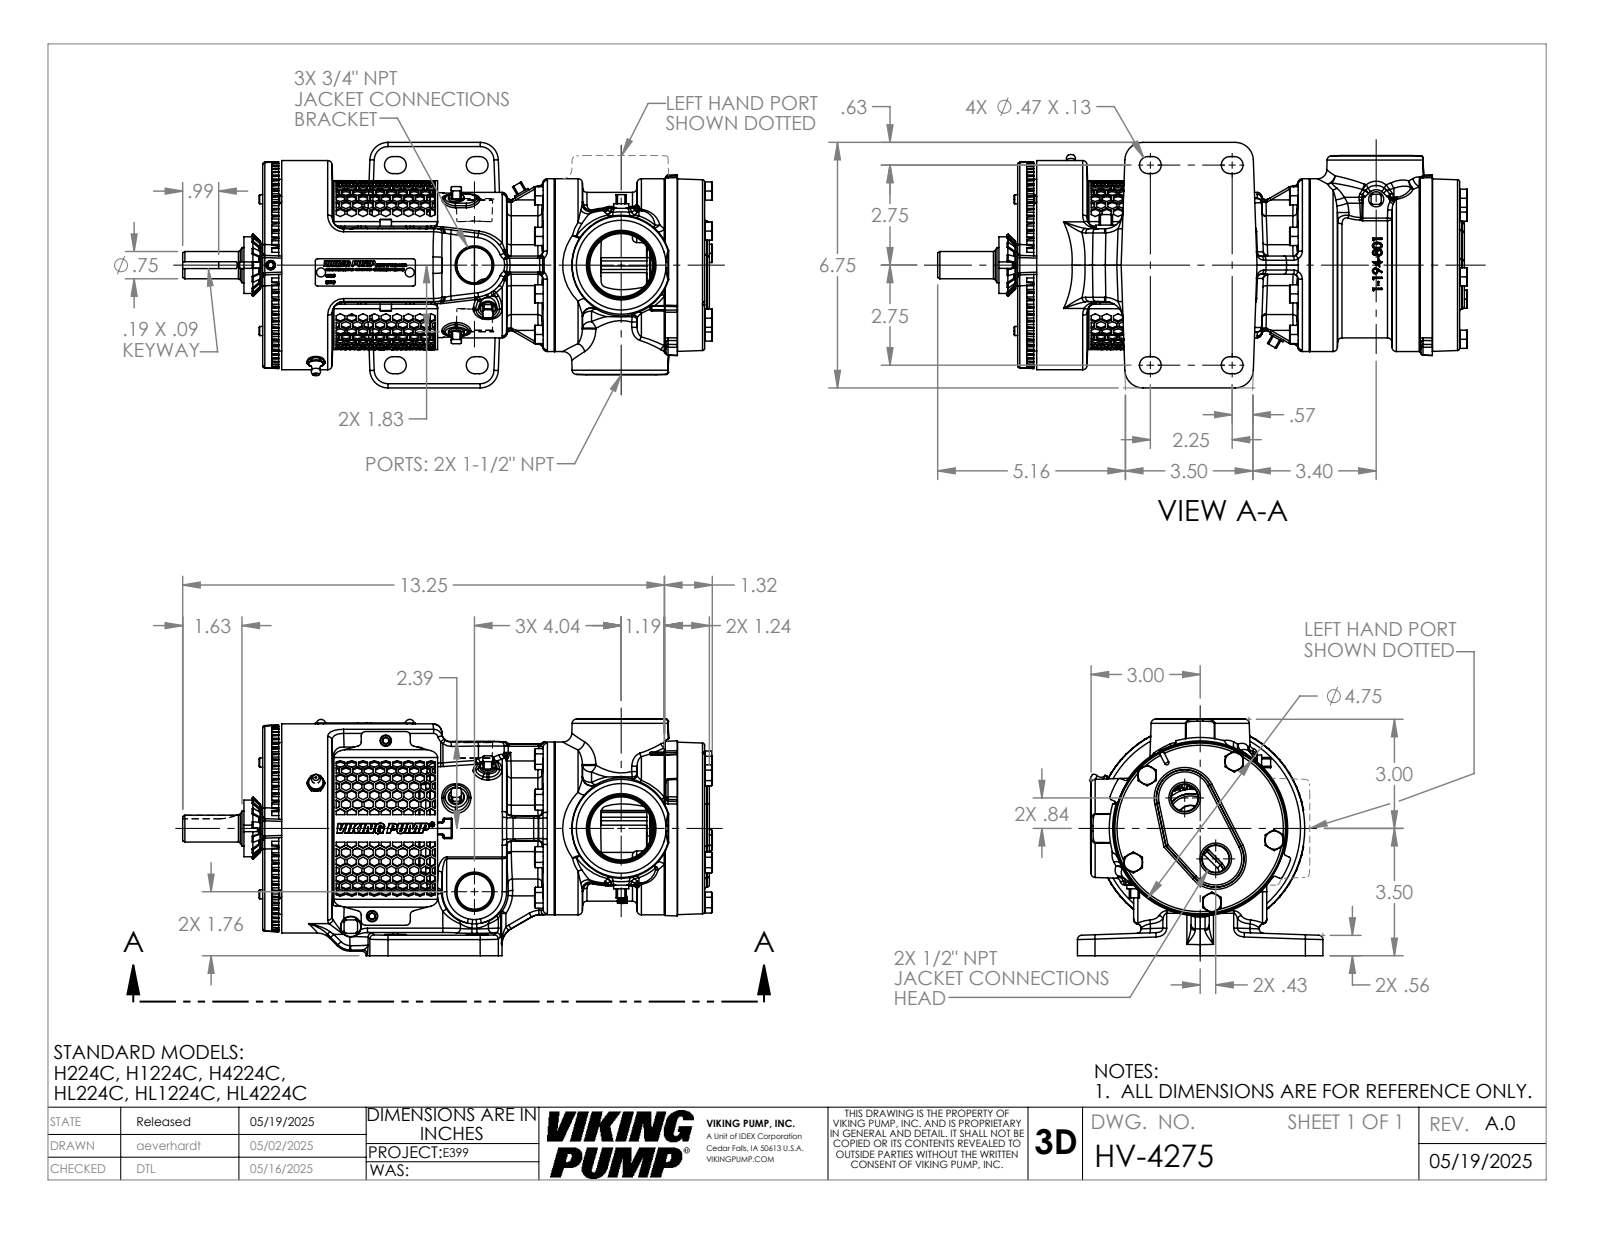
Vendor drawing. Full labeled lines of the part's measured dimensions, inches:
Part name (STEP PRODUCT): HV-4275
STEP written by: SolidWorks 2024 (AUTOMOTIVE_DESIGN)
Units: inches
Bodies: 1 solid, 3884 faces (1235 planar, 768 cylindrical, 1881 other)
Overall size (bounding box): 14.564 × 6.75 × 6.515
Volume: 195.2 in³ · Surface area: 497.4 in²
Round holes (diameter × count): ⌀0.25 ×6, ⌀0.159 ×3, ⌀0.257 ×2, ⌀0.986 ×1, ⌀0.989 ×1, ⌀4.502 ×1
Round bosses / shafts (diameter × count): ⌀0.5 ×5, ⌀0.437 ×3, ⌀0.312 ×3, ⌀0.25 ×2, ⌀5.75 ×1, ⌀4.75 ×1, ⌀4.747 ×1, ⌀4.499 ×1
Partial cylindrical surfaces — rounded edges, fillets, slot ends (radius × count): R0.054 ×140, R0.12 ×77, R0.06 ×50, R0.5 ×26, R0.03 ×22, R0.25 ×10, R0.234 ×8, R0.422 ×8
Main face-to-face distances: 1.94, 12.154, 10.213, 0.524, 1.417, 11.63, 0.44, 0.083, 1.5, 11.713
Hole centre spacings: 2.56, 4.434, 5.12, 4.84, 0.75, 3.688, 3.98, 4.283
